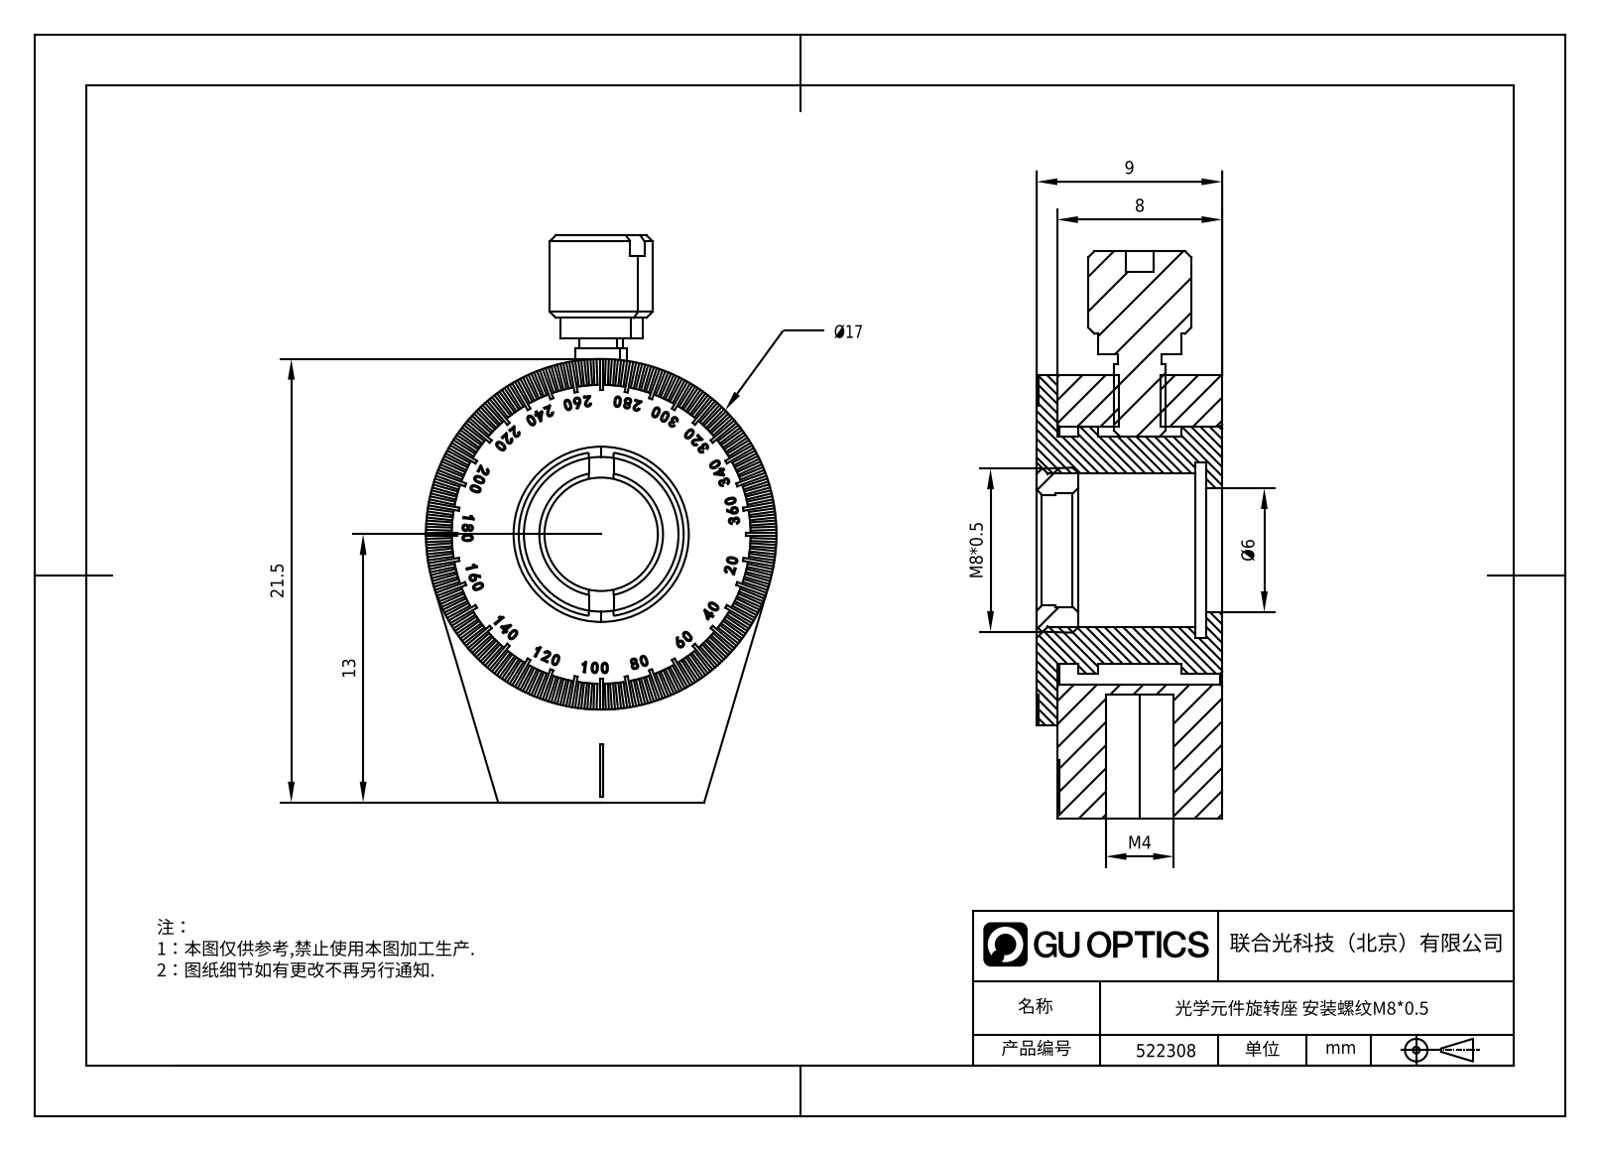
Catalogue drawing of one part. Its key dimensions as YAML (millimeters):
part_name: "一体式手拧螺丝_M2.5X4; ZFK透镜卡环压圈_1.8.5.8-ZFK-K7"
step_written_by: "SolidWorks 2021 (CONFIG_CONTROL_DESIGN)"
units: millimeters
bodies: {solids: 4, faces: 1227, planar: 992, cylindrical: 37, other: 198}
overall_size: [27.5, 17, 9]
volume: 2151
surface_area: 2606
round_holes:
  - {diameter: 2.05, count: 1}
  - {diameter: 3.3, count: 1}
  - {diameter: 5.5, count: 1}
  - {diameter: 6, count: 1}
  - {diameter: 7.5, count: 1}
  - {diameter: 8.5, count: 1}
round_bosses_or_shafts:
  - {diameter: 17, count: 1}
  - {diameter: 12, count: 1}
  - {diameter: 11, count: 1}
  - {diameter: 8, count: 1}
  - {diameter: 5, count: 1}
  - {diameter: 4, count: 1}
  - {diameter: 2.5, count: 1}
  - {diameter: 2.1, count: 1}
partial_cylinders:
  - {radius: 5, count: 1}
face_to_face_distances: [8, 1, 9, 2, 7, 6, 0.9, 8.9, 1.9, 0.8]
